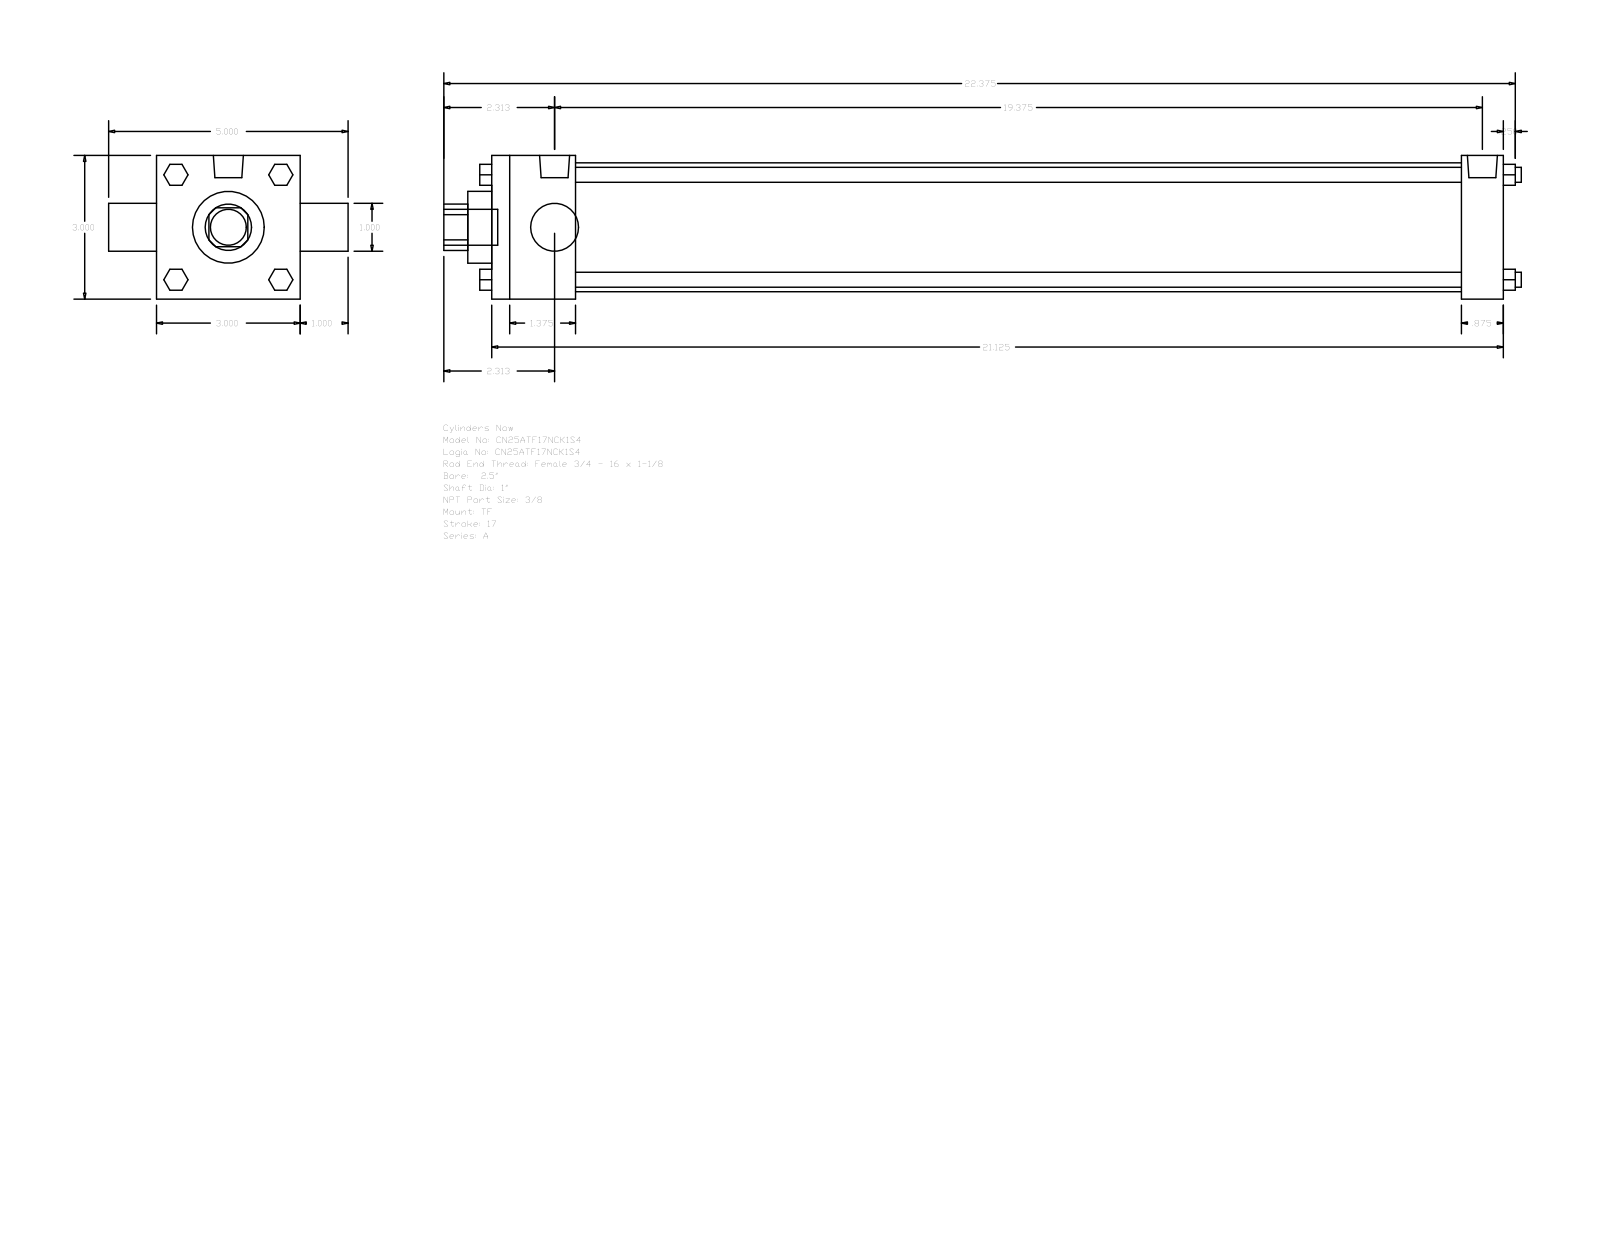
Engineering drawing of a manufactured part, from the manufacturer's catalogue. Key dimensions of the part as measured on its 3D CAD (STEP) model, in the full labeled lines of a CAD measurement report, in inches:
Part name (STEP PRODUCT): A_TF__0250_1
STEP written by: GSSL Pune (CONFIG_CONTROL_DESIGN)
Units: inches
Bodies: 0 solids, 120 faces (92 planar, 28 cylindrical, 0 other)
Overall size (bounding box): 22.5 × 5 × 3
Round holes (diameter × count): ⌀1 ×2, ⌀1.5 ×1, ⌀2.69 ×1
Round bosses / shafts (diameter × count): ⌀0.313 ×4, ⌀0.219 ×3, ⌀0.627 ×2, ⌀0.75 ×1
Partial cylindrical surfaces — rounded edges, fillets, slot ends (radius × count): R0.484 ×1
Main face-to-face distances: 3, 21.125, 1.75, 20.25, 18.5, 19.375, 0.875, 1, 4, 21.625
